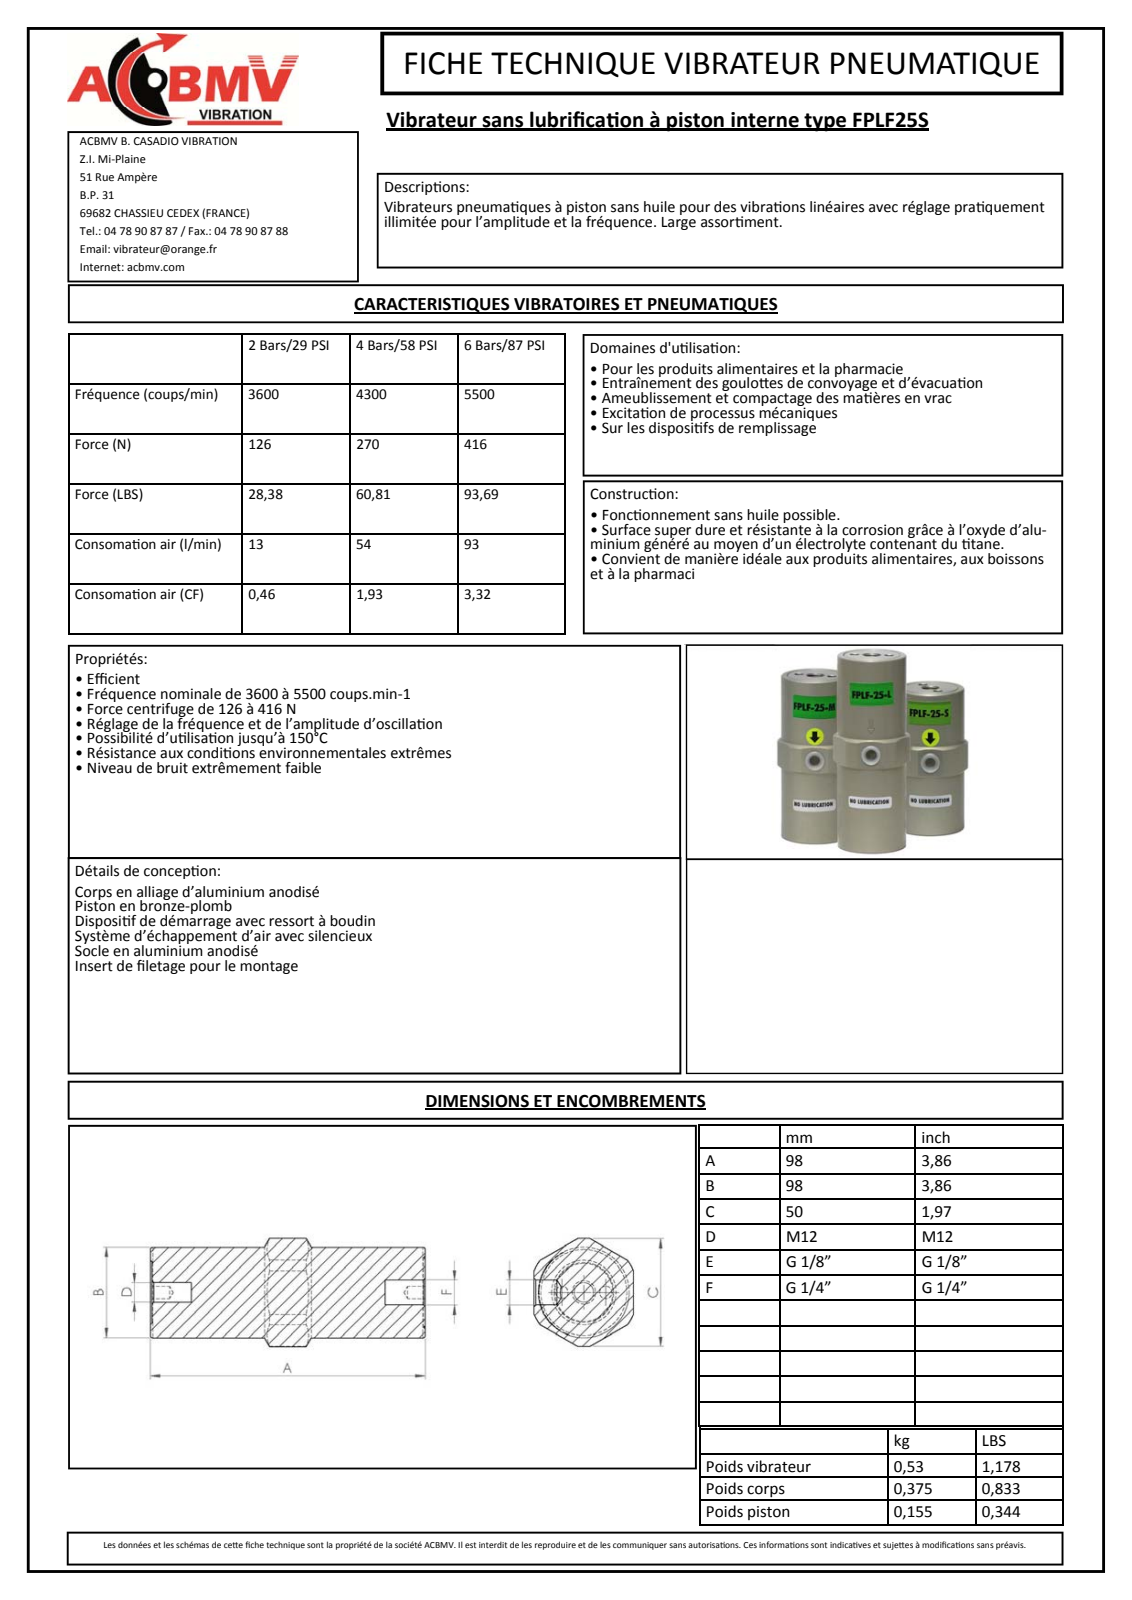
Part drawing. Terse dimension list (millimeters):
name: 9525-10-M
written by: Autodesk Inventor 2011 (CONFIG_CONTROL_DESIGN)
unit: mm
bodies: 1 solid, 485 faces (181 planar, 63 cylindrical, 241 other)
size: 98 × 53.5 × 50
volume: 177 968 mm³; area: 20 996 mm²
holes: 4× ⌀6.2, 1× ⌀2.5, 1× ⌀8.57, 1× ⌀10.11, 1× ⌀11.45
bosses: 1× ⌀48
rounds: 1× R14.5, 1× R23.8, 1× R24.08, 1× R24.1, 1× R26.75
face distances: 50, 98, 0.5, 97.5, 13.7, 84.3, 83.8, 79, 19, 18.5
hole spacings: 1, 11, 12, 23, 22, 24
